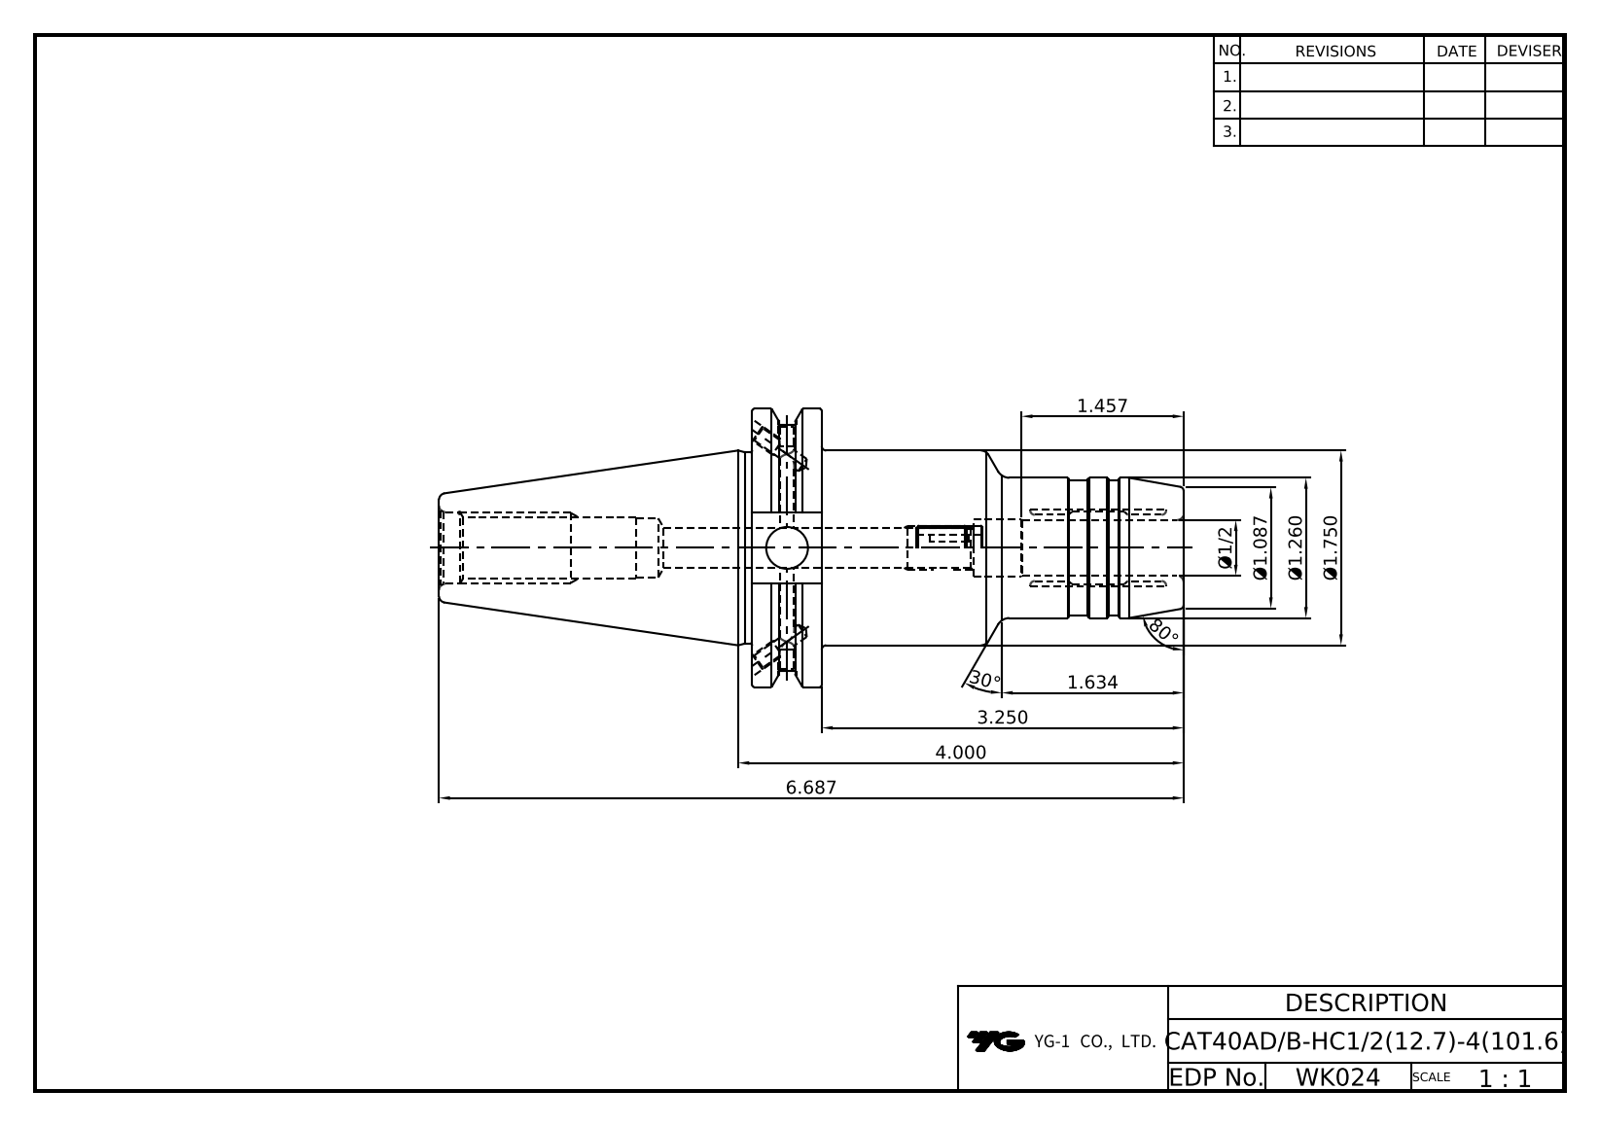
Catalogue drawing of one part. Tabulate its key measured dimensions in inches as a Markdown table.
| quantity | value |
| --- | --- |
| part name | CAT40ADB-SHANK |
| STEP written by | CREO PARAMETRIC BY PTC INC, 2018500 (CONFIG_CONTROL_DESIGN) |
| units | inches |
| bodies | 1 solid, 138 faces (36 planar, 36 cylindrical, 66 other) |
| overall size | 6.688 × 2.5 × 2.395 |
| volume | 11.56 in³ |
| surface area | 52.95 in² |
| round holes (diameter × count) | 0.358 × 1, 0.375 × 1, 0.394 × 1, 0.5 × 1, 0.52 × 1, 0.531 × 1, 0.625 × 1, 0.642 × 1 |
| round bosses / shafts (diameter × count) | 2.5 × 1, 2.217 × 1, 1.75 × 1, 1.717 × 1, 1.26 × 1, 1.22 × 1 |
| main face-to-face distances | 0.626, 3.876, 3.25, 1.874, 2.812, 3.438, 6.688, 0.645, 3.05, 0.238 |
